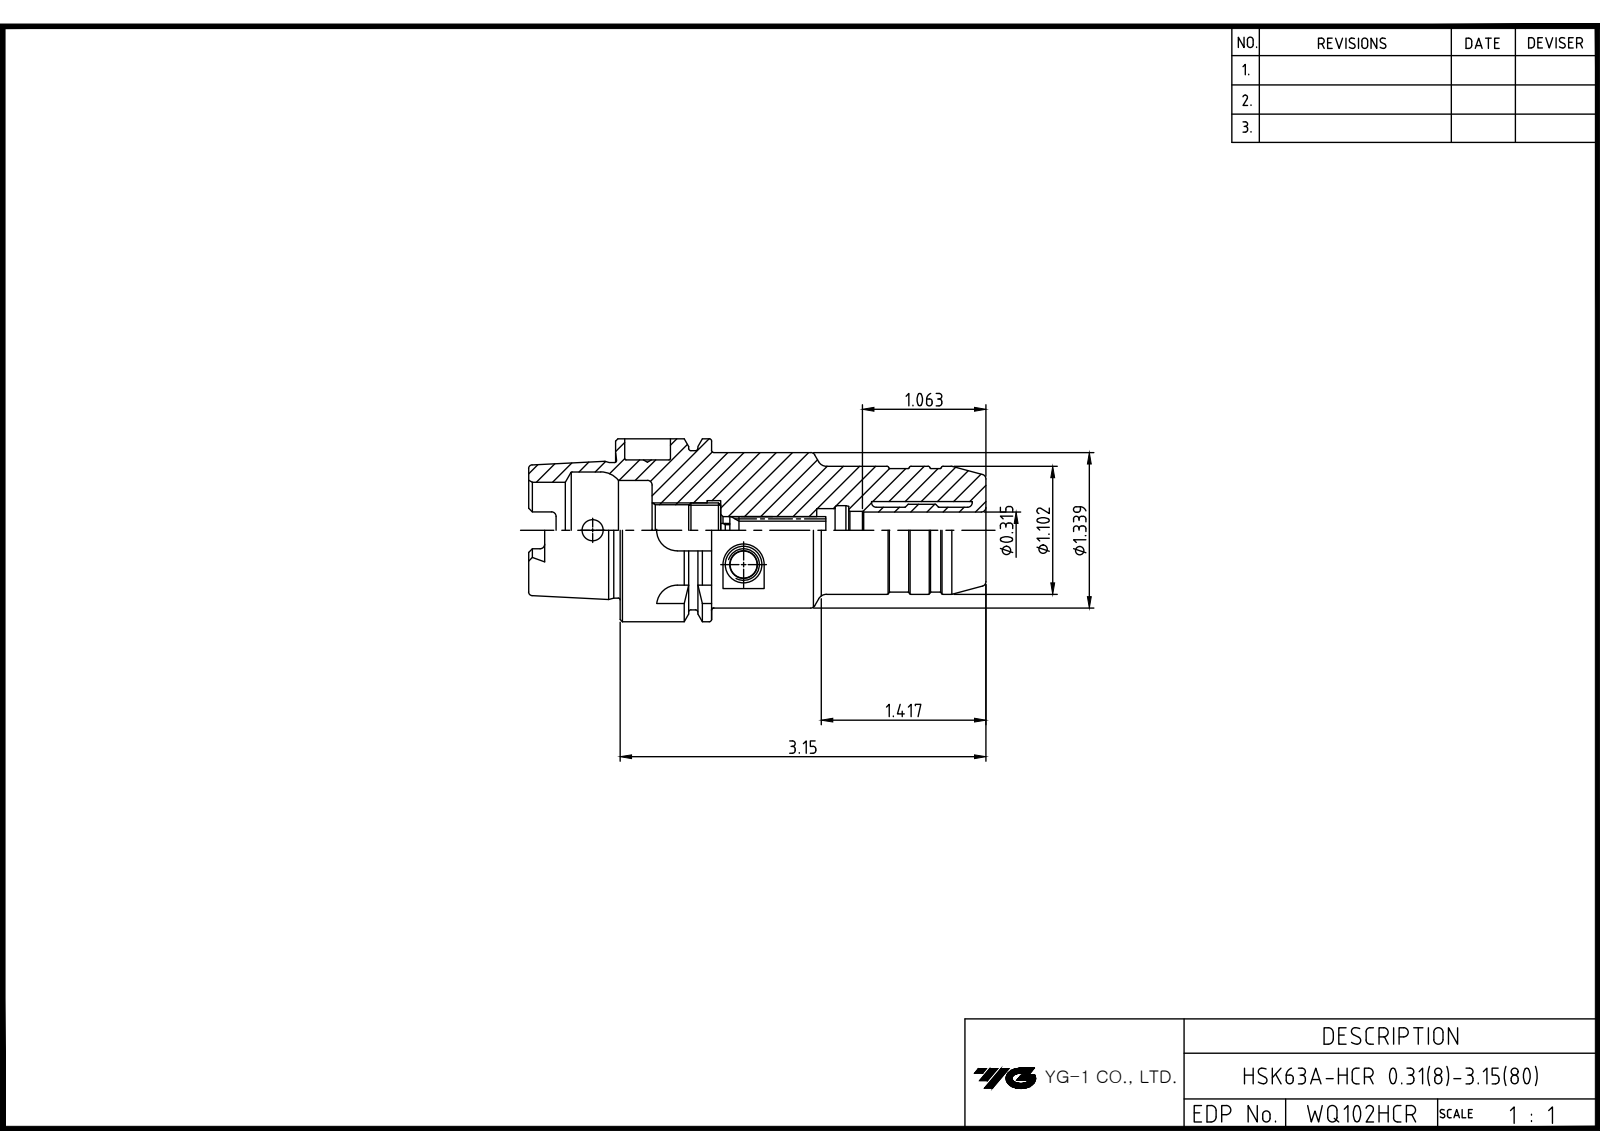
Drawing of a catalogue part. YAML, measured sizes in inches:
part_name: "HSK63A-HCR8-80"
step_written_by: "Autodesk Inventor 2020 (AUTOMOTIVE_DESIGN)"
units: inches
bodies: {solids: 1, faces: 134, planar: 42, cylindrical: 38, other: 54}
overall_size: [4.409, 2.48, 2.48]
volume: 8.211
surface_area: 44.66
round_holes:
  - {diameter: 0.244, count: 1}
  - {diameter: 0.295, count: 1}
  - {diameter: 0.315, count: 1}
  - {diameter: 0.339, count: 1}
  - {diameter: 0.394, count: 1}
  - {diameter: 0.666, count: 1}
  - {diameter: 0.748, count: 1}
  - {diameter: 1.339, count: 1}
  - {diameter: 1.575, count: 1}
round_bosses_or_shafts:
  - {diameter: 2.48, count: 1}
  - {diameter: 2.165, count: 1}
  - {diameter: 1.969, count: 1}
  - {diameter: 1.891, count: 1}
  - {diameter: 1.102, count: 1}
  - {diameter: 1.063, count: 1}
partial_cylinders:
  - {radius: 0.059, count: 6}
  - {radius: 0.113, count: 4}
  - {radius: 0.315, count: 4}
face_to_face_distances: [1.024, 0.394, 0.63, 1.26, 3.15, 2.756, 2.126, 1.654, 2.283, 4.409]
